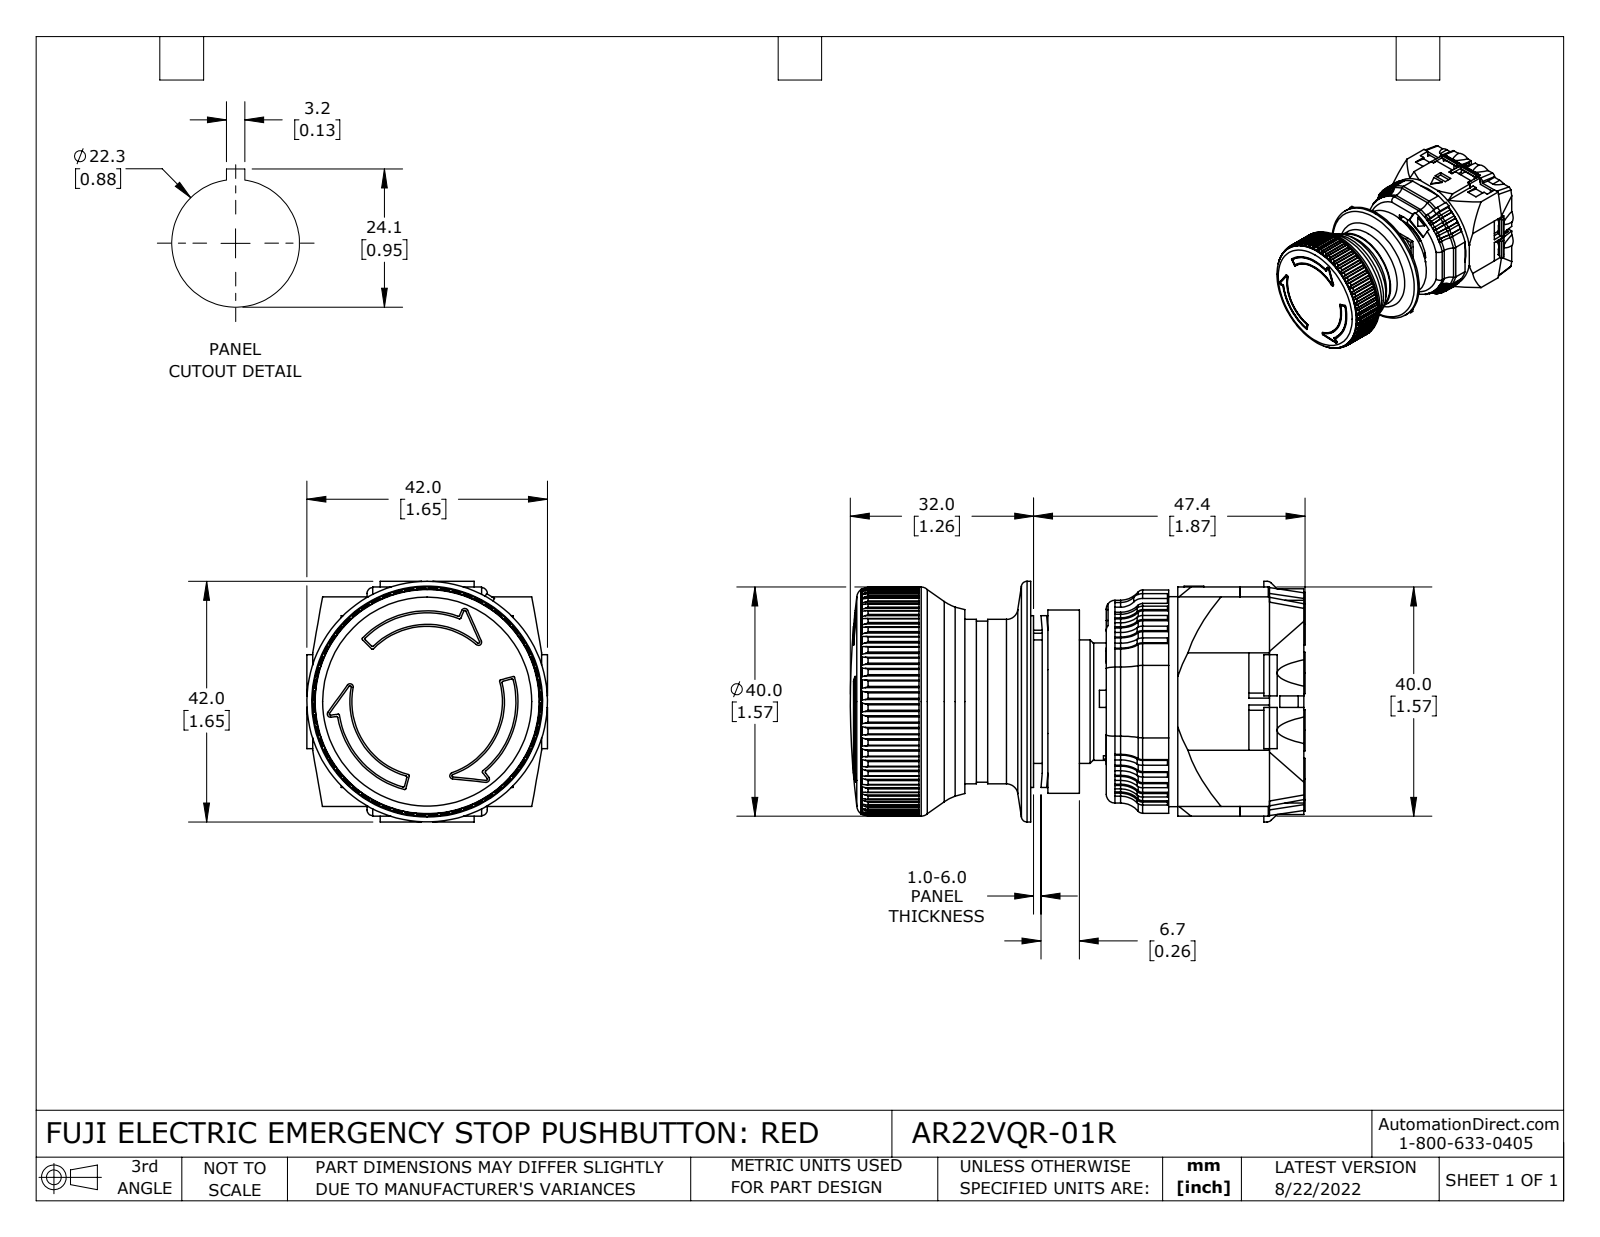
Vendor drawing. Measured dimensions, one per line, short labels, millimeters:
name: AR22VQR-01R
written by: SolidWorks 2021 (CONFIG_CONTROL_DESIGN)
unit: mm
bodies: 8 solids, 1459 faces (645 planar, 600 cylindrical, 214 other)
size: 79.4 × 42 × 42
volume: 62 430 mm³; area: 34 710 mm²
holes: 12× ⌀3.5, 12× ⌀6.2, 1× ⌀8, 1× ⌀17.5, 1× ⌀21, 1× ⌀21.3, 1× ⌀22, 1× ⌀22.3, 1× ⌀28, 1× ⌀29.7, 1× ⌀36.7
bosses: 12× ⌀7.2, 1× ⌀42, 1× ⌀40, 1× ⌀32, 1× ⌀30, 1× ⌀28.7, 1× ⌀28.1, 1× ⌀22.4
rounds: 146× R0.2, 64× R0.4, 19× R1.2, 19× R3.8, 12× R4.2, 10× R1, 6× R0.6, 4× R1.5
face distances: 1, 18.5, 11.5, 10, 44.7, 18, 21, 3, 23.6, 4
hole spacings: 16.3, 23, 8.3, 8.9, 10, 14.9, 18.1, 18.7
